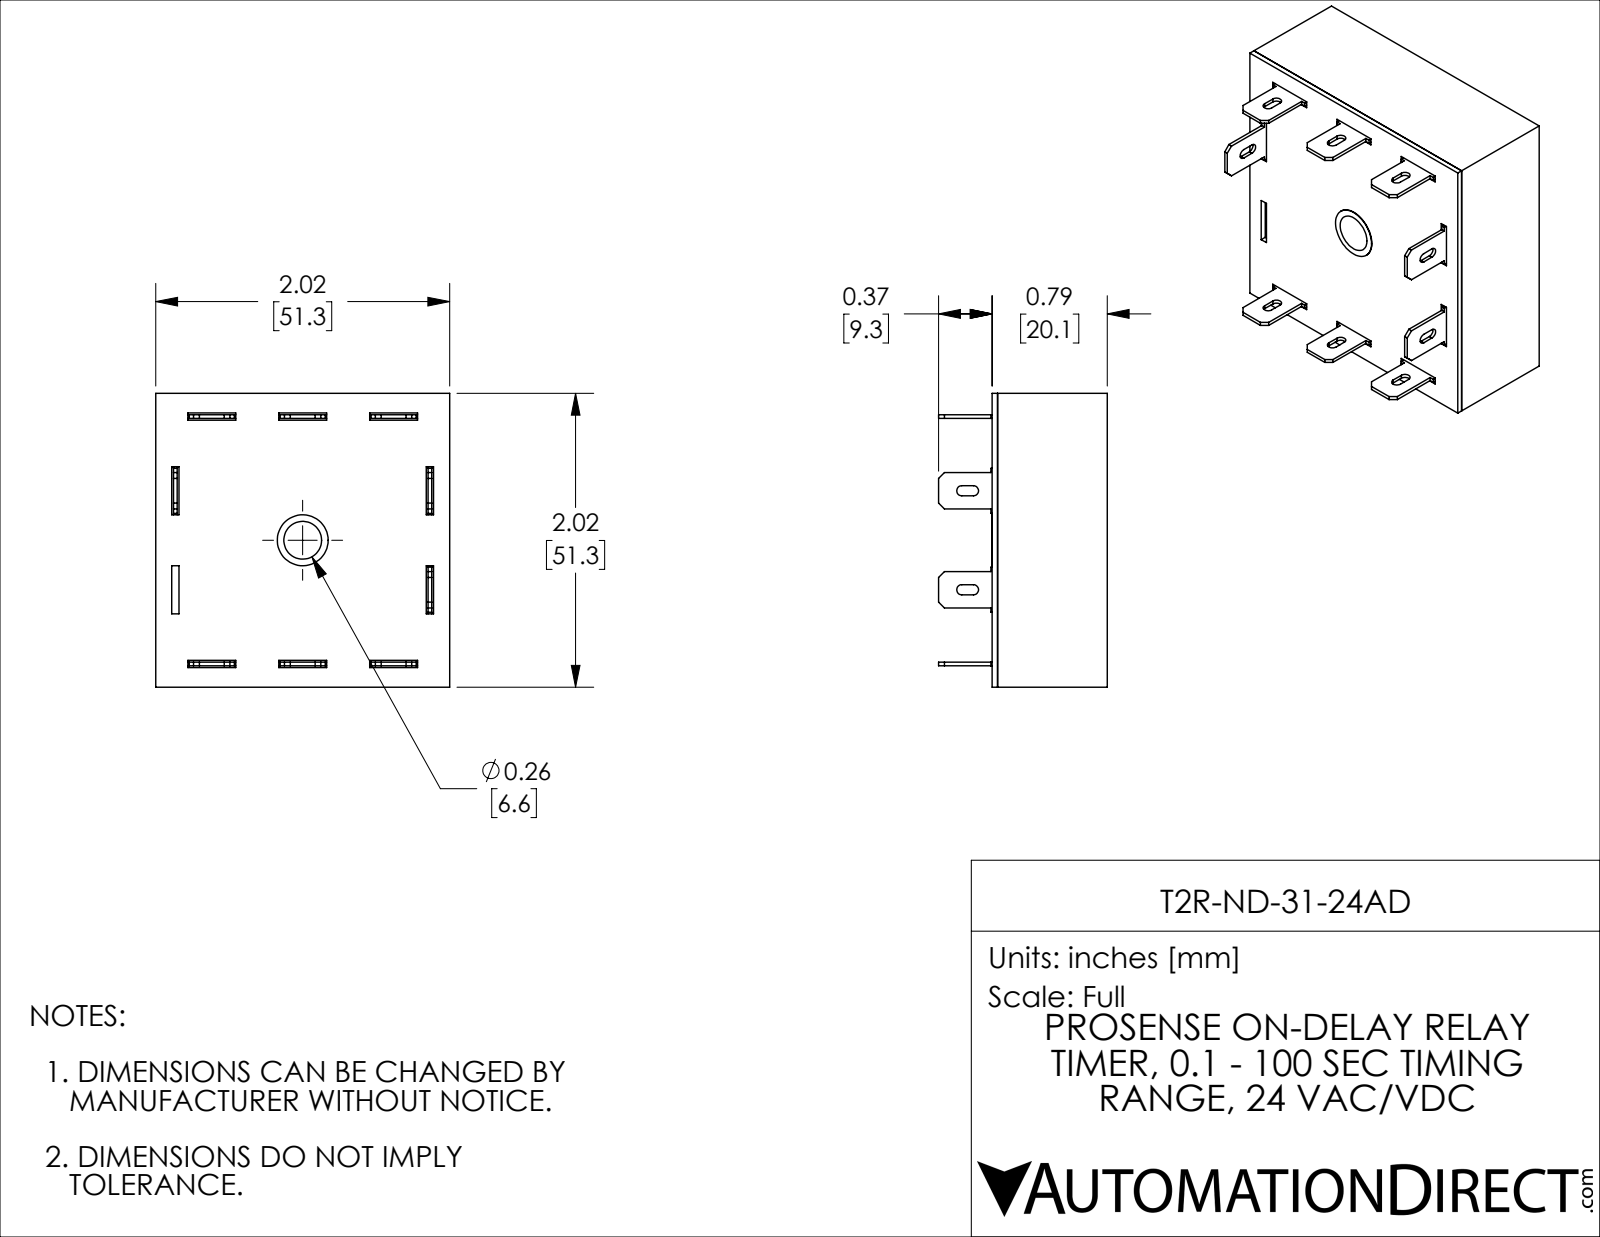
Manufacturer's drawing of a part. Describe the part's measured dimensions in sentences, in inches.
The part is named "T2R-ND-31-24AD". Its 3-D file was written by "SolidWorks 2021 (CONFIG_CONTROL_DESIGN)". It is 11 solids with 280 faces: 256 planar, 22 cylindrical and 2 other. Overall it measures 2.02 by 2.02 by 1.16 inches. Its volume is 0.682 cubic inches and its surface area 36.12 square inches. Round holes: 1 of diameter 0.35. Partial cylindrical surfaces (rounded edges, fillets, slot ends): 10 of radius 0.035. The main face-to-face distances are 0.045, 1.975, 0.754, 0.792, 0.038, 0.709, 0.747, 2.02, 0.147, 1.872.
